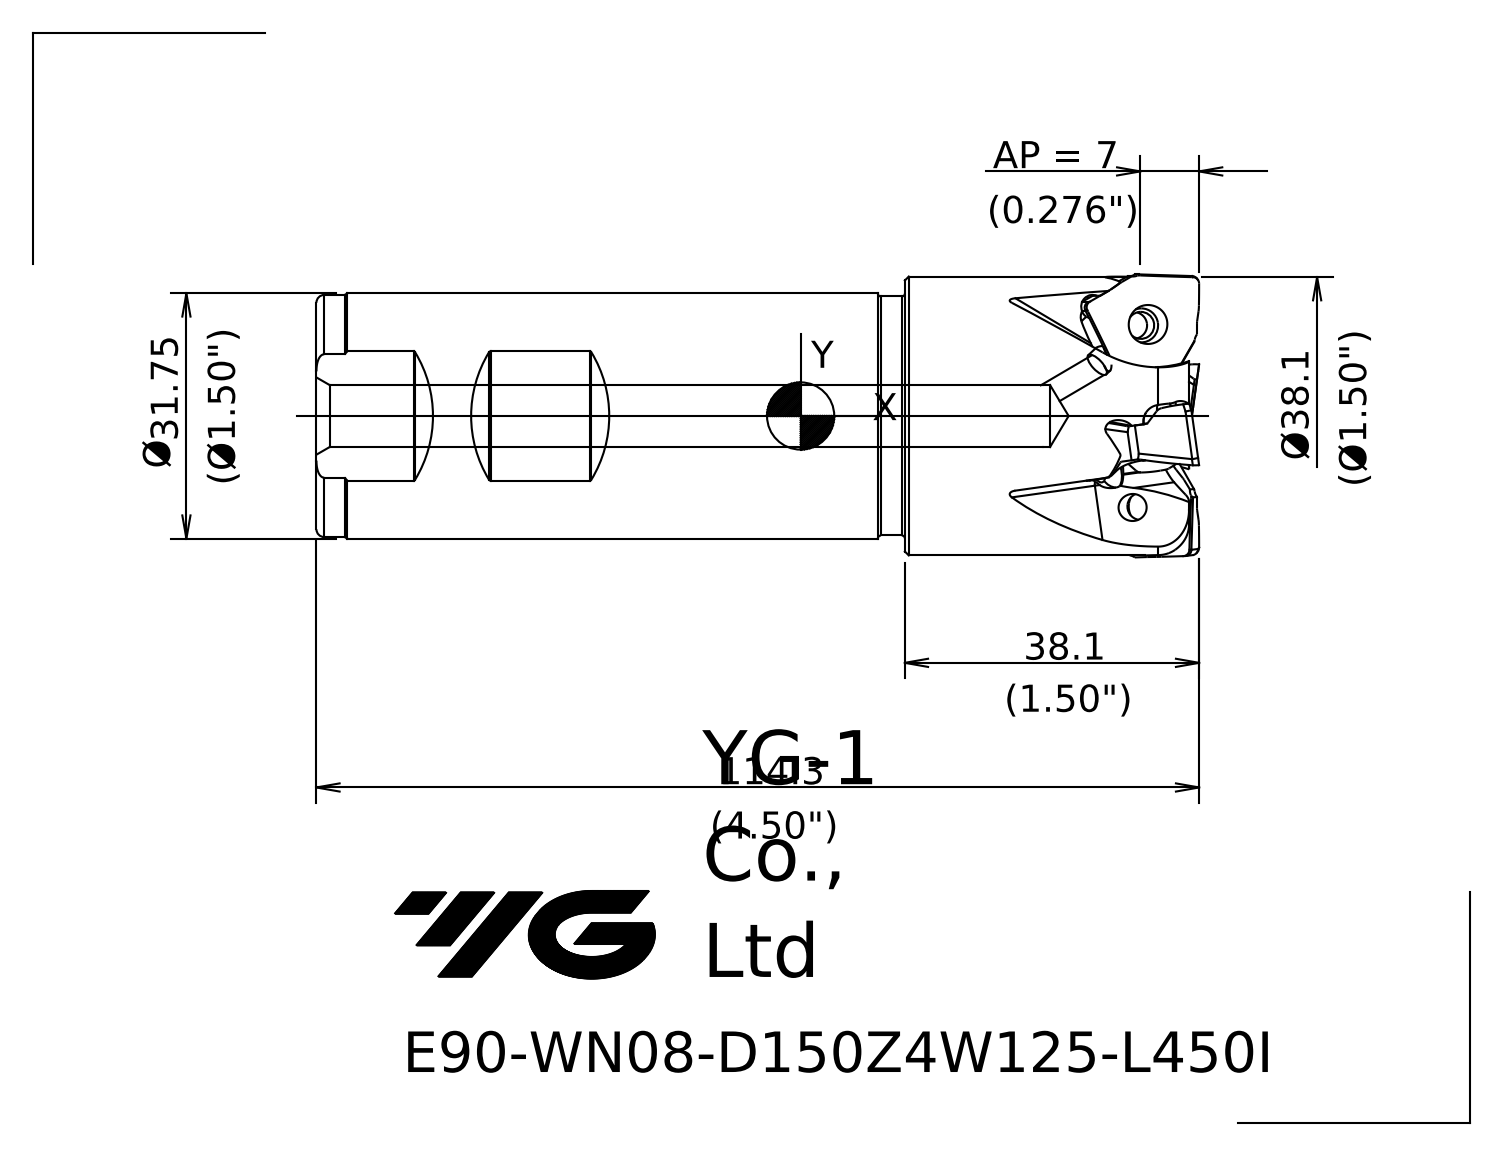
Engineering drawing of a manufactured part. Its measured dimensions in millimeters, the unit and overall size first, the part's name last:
Units: millimetres
Overall size (bounding box): 114.3 × 38.1 × 38.1
Round holes (diameter × count): ⌀8 ×1
Round bosses / shafts (diameter × count): ⌀36.1 ×1, ⌀31.75 ×1, ⌀31.35 ×1, ⌀30.95 ×1
Partial cylindrical surfaces — rounded edges, fillets, slot ends (radius × count): R0.3 ×3
Main face-to-face distances: 76.2, 36.8, 113, 4.2, 32.6, 108.8, 16.14
Volume: 90 681 mm³ · Surface area: 19 815 mm²
Bodies: 1 solid, 67 faces (9 planar, 8 cylindrical, 50 other)
Part name (STEP PRODUCT): 10224990B0573zb4
STEP written by: SIEMENS PLM Software NX 10.0 (AP203_CONFIGURATION_CONTROLLED_3D_DESIGN_OF_MECHANICAL_PARTS_AND_ASSEMBLIES_MIM_LF)
